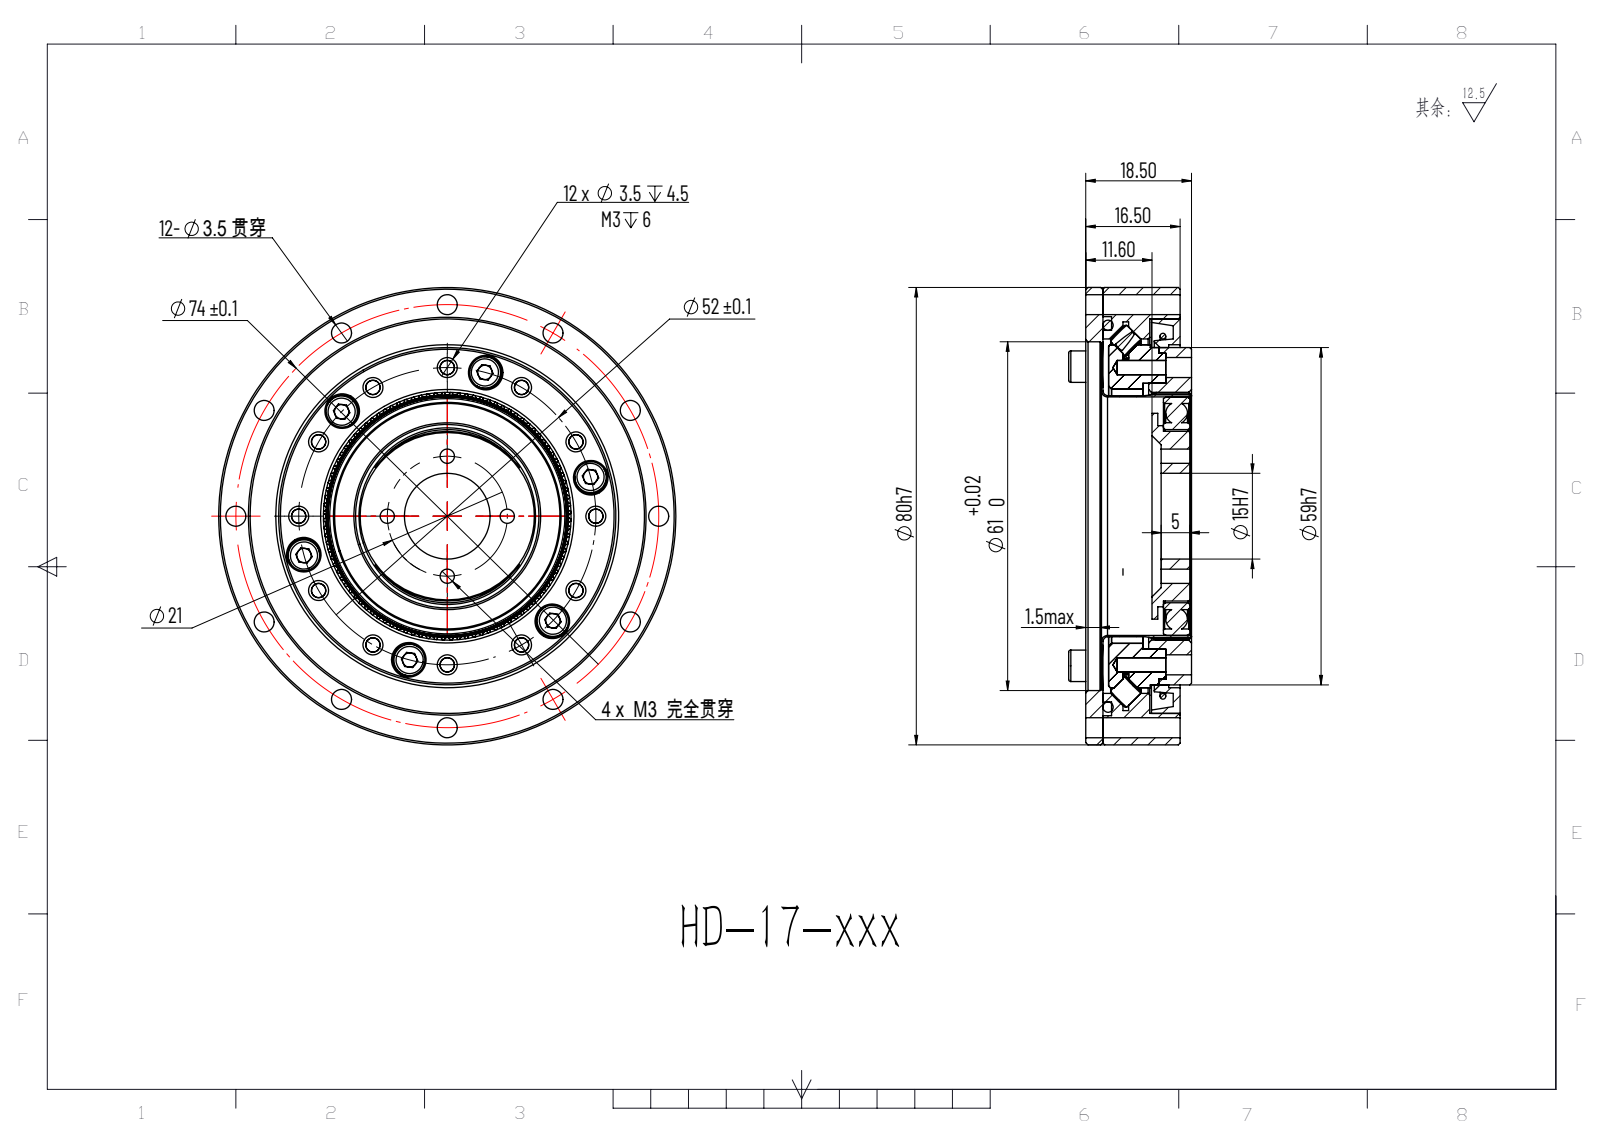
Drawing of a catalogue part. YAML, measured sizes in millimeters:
part_name: "HD-17-xxx; hexagon socket head cap screws gb_GB_FASTENER_SCREWS_HSHCS M3X8-C; HD-17-??; HD-17-???? <1> (+7 more)"
step_written_by: "ONSHAPE BY PTC INC, 1.201 (AP242_MANAGED_MODEL_BASED_3D_ENGINEERING_MIM_LF)"
units: millimeters
bodies: {solids: 68, faces: 2566, planar: 719, cylindrical: 1420, other: 427}
overall_size: [80, 80, 21.5]
volume: 63479
surface_area: 65542
round_holes:
  - {diameter: 3.5, count: 28}
  - {diameter: 2.5, count: 26}
  - {diameter: 3.4, count: 6}
  - {diameter: 5.6, count: 6}
  - {diameter: 1.6, count: 1}
  - {diameter: 2.4, count: 1}
  - {diameter: 4.3, count: 1}
  - {diameter: 15, count: 1}
  - {diameter: 30.3, count: 1}
  - {diameter: 39.44, count: 1}
  - {diameter: 41.72, count: 1}
  - {diameter: 44.5, count: 1}
round_bosses_or_shafts:
  - {diameter: 4, count: 46}
  - {diameter: 5.5, count: 10}
  - {diameter: 3, count: 10}
  - {diameter: 80, count: 1}
  - {diameter: 65, count: 1}
  - {diameter: 60, count: 1}
  - {diameter: 57, count: 1}
  - {diameter: 55, count: 1}
partial_cylinders:
  - {radius: 0.27, count: 204}
  - {radius: 1.83, count: 204}
  - {radius: 0.27, count: 200}
  - {radius: 0.3, count: 200}
  - {radius: 0.12, count: 102}
  - {radius: 21.22, count: 1}
  - {radius: 21.67, count: 1}
  - {radius: 21.76, count: 1}
face_to_face_distances: [1, 10, 11, 2.5, 3, 14, 4.5, 13.5, 12.5, 2]
hole_center_spacings: [26, 19.46, 32.91, 45.22, 60.92, 37, 54.84, 13.46]
